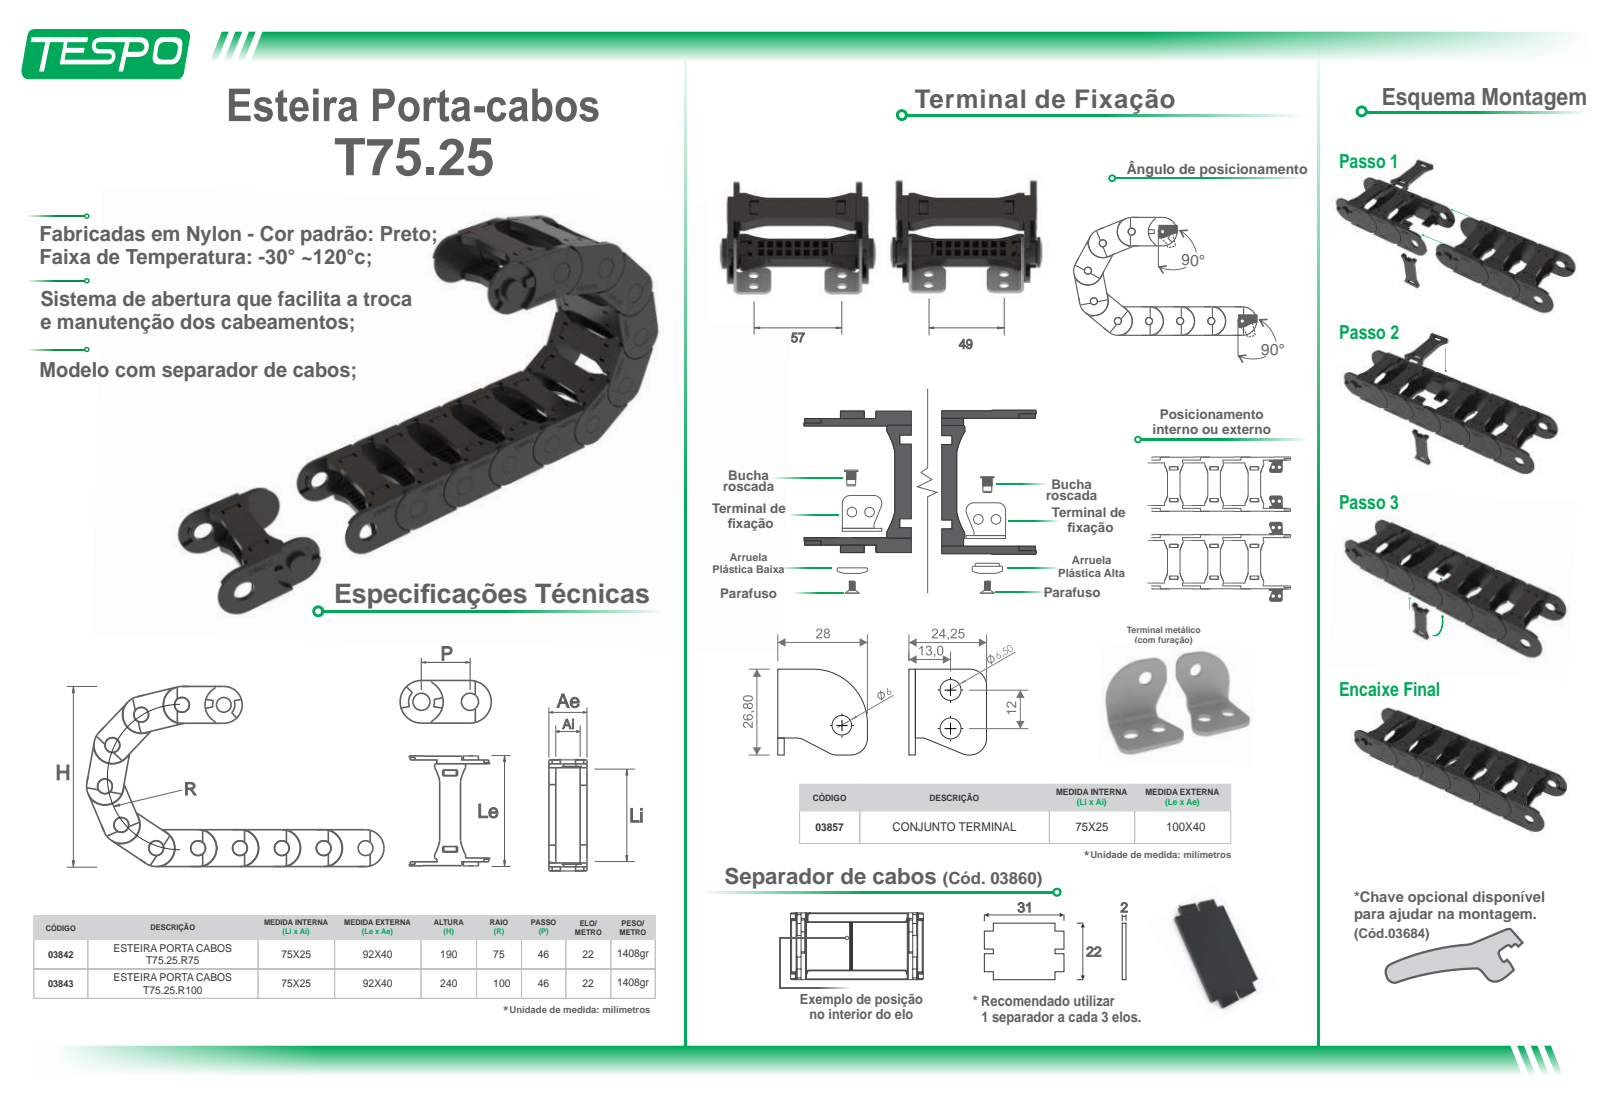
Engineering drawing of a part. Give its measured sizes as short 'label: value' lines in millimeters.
written by: ST-DEVELOPER v15 (AUTOMOTIVE_DESIGN)
unit: mm
bodies: 4 solids, 155 faces (92 planar, 0 cylindrical, 63 other)
size: 91.78 × 85.5 × 40
volume: 54 981 mm³; area: 28 647 mm²
face distances: 4.05, 83.08, 79.03, 8.1, 87.13, 7.2, 32.8, 40, 74.98, 91.18
